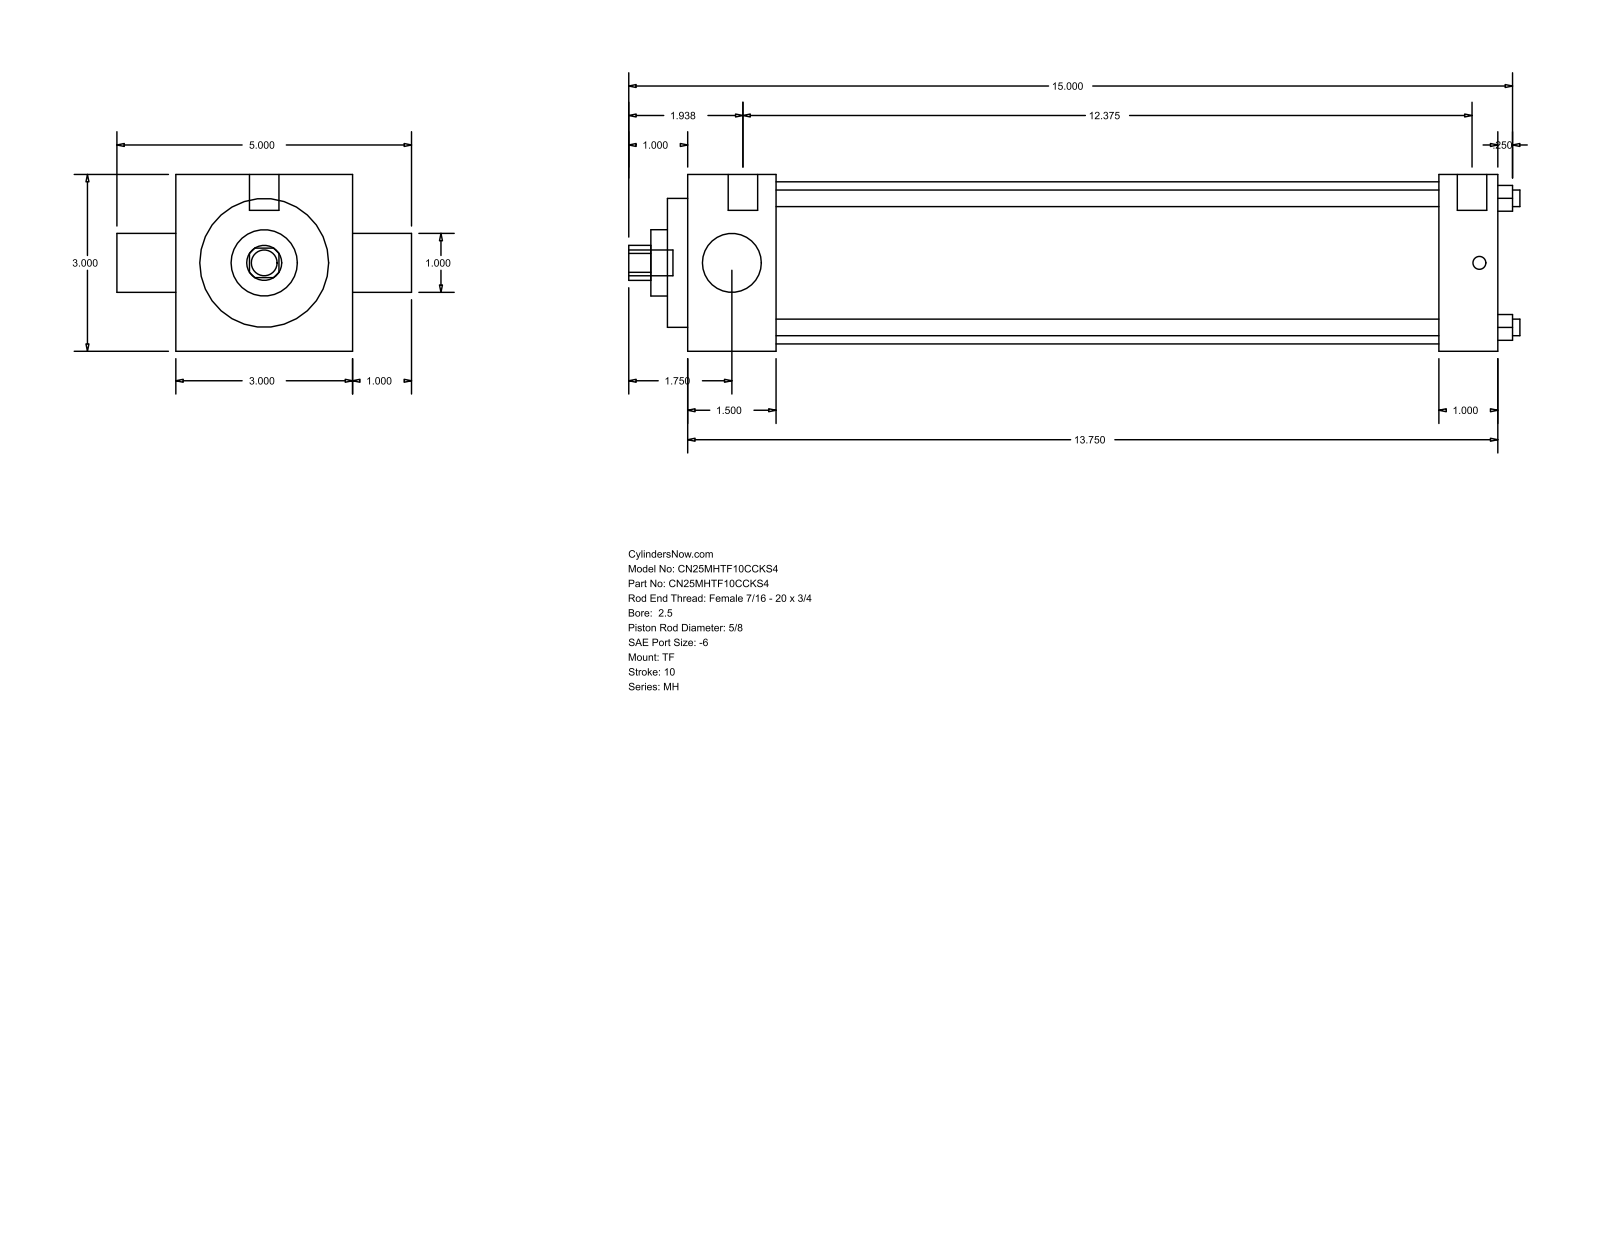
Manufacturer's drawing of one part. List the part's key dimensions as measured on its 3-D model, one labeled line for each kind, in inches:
Part name (STEP PRODUCT): MH_TF__0250_0.625
STEP written by: GSSL Pune (CONFIG_CONTROL_DESIGN)
Units: inches
Bodies: 0 solids, 86 faces (61 planar, 25 cylindrical, 0 other)
Overall size (bounding box): 15.125 × 5 × 3
Round holes (diameter × count): ⌀0.281 ×4, ⌀0.625 ×1, ⌀1 ×1, ⌀1.125 ×1, ⌀2.187 ×1, ⌀2.75 ×1
Round bosses / shafts (diameter × count): ⌀0.219 ×3, ⌀0.5 ×2, ⌀0.437 ×1
Partial cylindrical surfaces — rounded edges, fillets, slot ends (radius × count): R0.297 ×1
Main face-to-face distances: 3, 13.75, 1, 1.5, 12.25, 12.75, 11.25, 0.344, 1.844, 13.094
Hole centre spacings: 1.548, 2.19, 3.097
